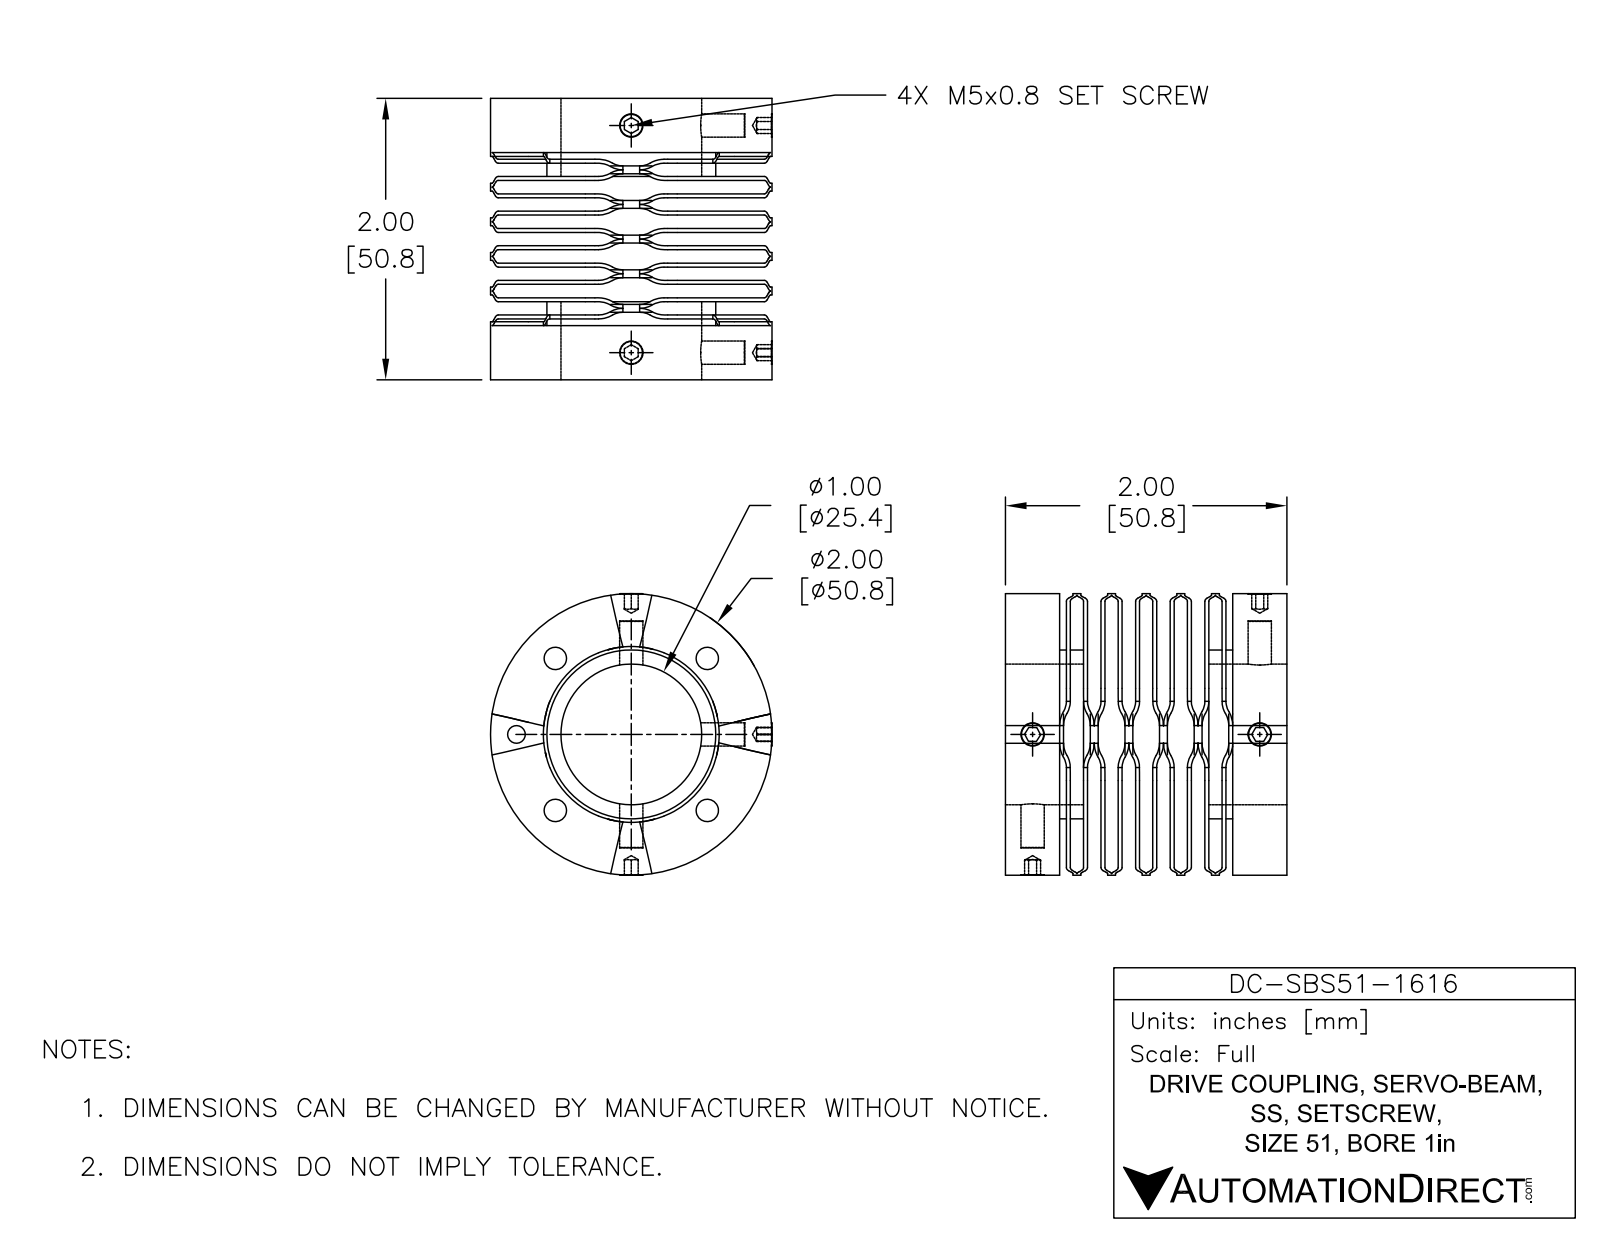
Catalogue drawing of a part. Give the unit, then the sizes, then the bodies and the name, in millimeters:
Units: millimetres
Overall size (bounding box): 51.1 × 50.95 × 50.76
Round holes (diameter × count): ⌀4.04 ×4, ⌀4.2 ×4, ⌀3.17 ×1, ⌀25.4 ×1, ⌀31.75 ×1
Round bosses / shafts (diameter × count): ⌀4.2 ×4, ⌀50.8 ×1, ⌀30.48 ×1
Partial cylindrical surfaces — rounded edges, fillets, slot ends (radius × count): R1.8 ×320
Main face-to-face distances: 6.24, 12.48, 18.72, 0.71, 3.09, 2.38, 6.95, 9.33, 8.62, 3.86
Hole centre spacings: 19.4, 27.44, 15.41, 37.08, 38.81, 20.73, 38.72
Volume: 40 230 mm³ · Surface area: 41 486 mm²
Bodies: 16 solids, 798 faces (362 planar, 428 cylindrical, 8 other)
Part name (STEP PRODUCT): DC-SBS51-1616
STEP written by: SolidWorks 2015 (AUTOMOTIVE_DESIGN)
